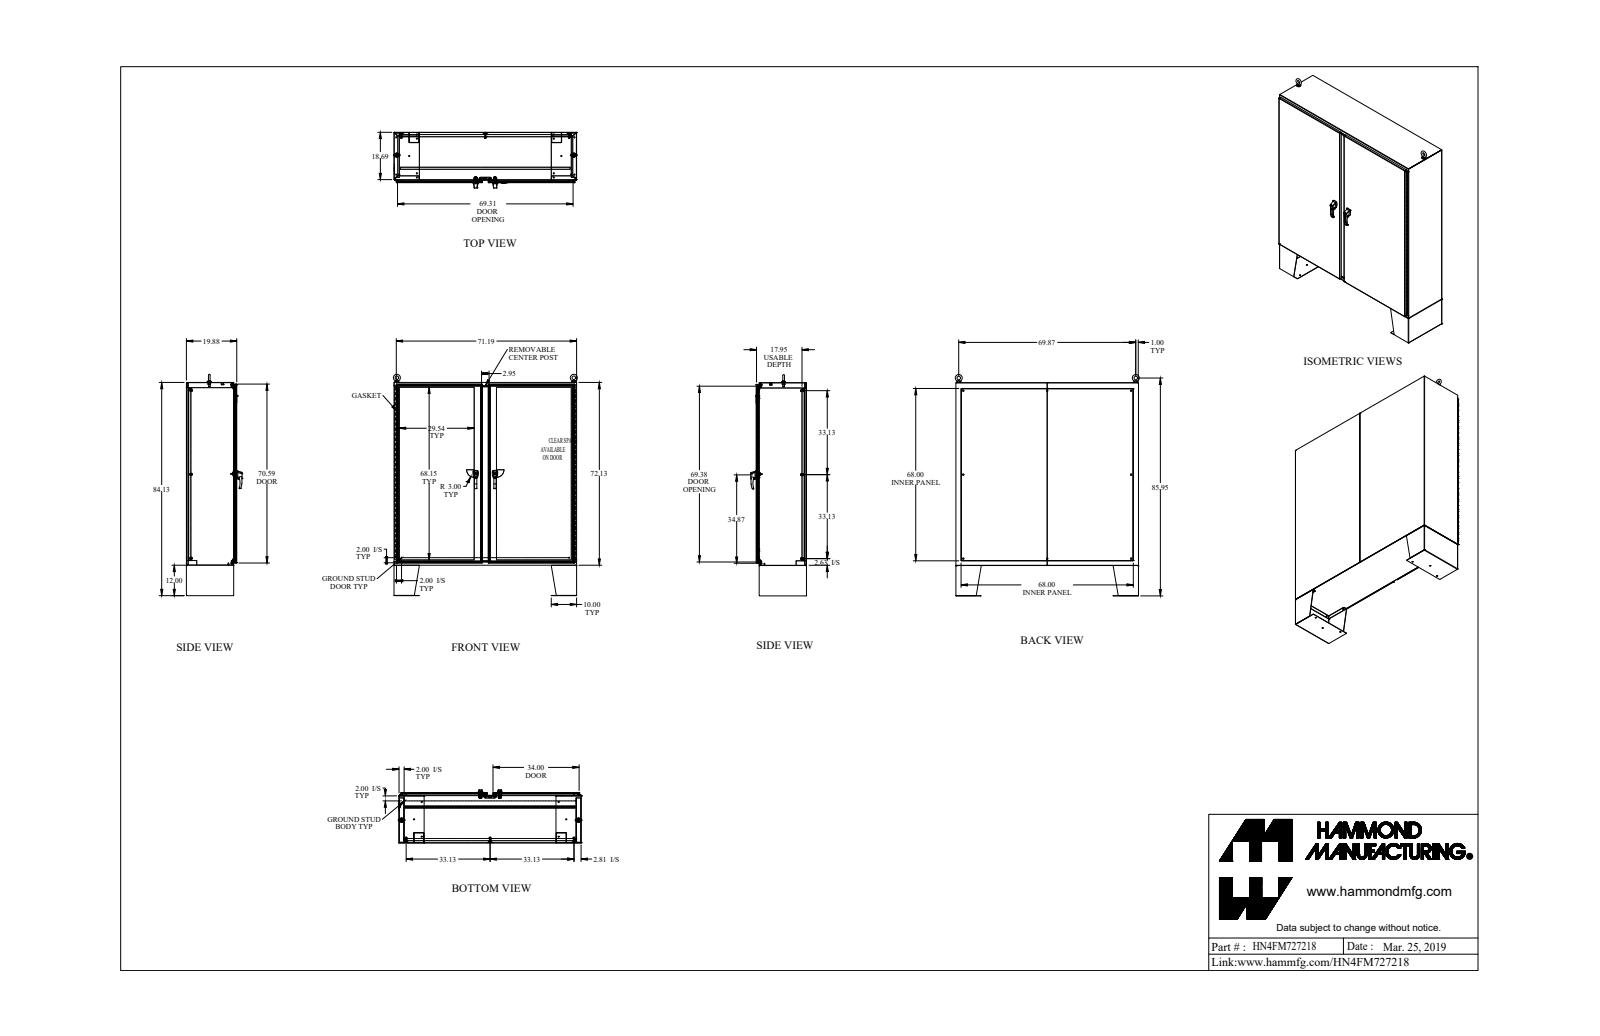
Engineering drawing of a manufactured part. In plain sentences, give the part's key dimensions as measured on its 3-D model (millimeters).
The part is named "HN4FM727218". Its 3-D file was written by "SolidWorks 2018 (AUTOMOTIVE_DESIGN)". It is 131 solids with 4006 faces: 1830 planar, 1803 cylindrical and 373 other. Overall it measures 2217.8 by 1844.2 by 558.5 millimeters. Its volume is 41 920 000 cubic millimeters and its surface area 33 020 000 square millimeters. Round holes: 24 of diameter 7.7, 14 of diameter 11.1, 8 of diameter 7.8, 8 of diameter 8.9, 8 of diameter 14.3, 6 of diameter 6.4, 6 of diameter 11.3, 4 of diameter 7.1, 4 of diameter 8, 4 of diameter 9.9, 3 of diameter 5.1, 3 of diameter 8. Round bosses or shafts: 10 of diameter 25.4, 8 of diameter 16.5, 8 of diameter 9.5, 8 of diameter 8.4, 8 of diameter 7.1, 4 of diameter 19.1, 4 of diameter 15.9, 4 of diameter 11.2. Partial cylindrical surfaces (rounded edges, fillets, slot ends): 33 of radius 12.7, 32 of radius 0.5, 32 of radius 3.2, 29 of radius 1.2, 29 of radius 3.6, 28 of radius 1.5, 12 of radius 0.8, 12 of radius 2.3. The main face-to-face distances are 2.4, 502.4, 500, 457.1, 3.2, 45.3, 42.8, 42.1, 39.7, 460.3. The hole center spacings are 152.4, 304.8, 457.2, 609.6, 1881.4, 762, 914.4, 1682.8.
